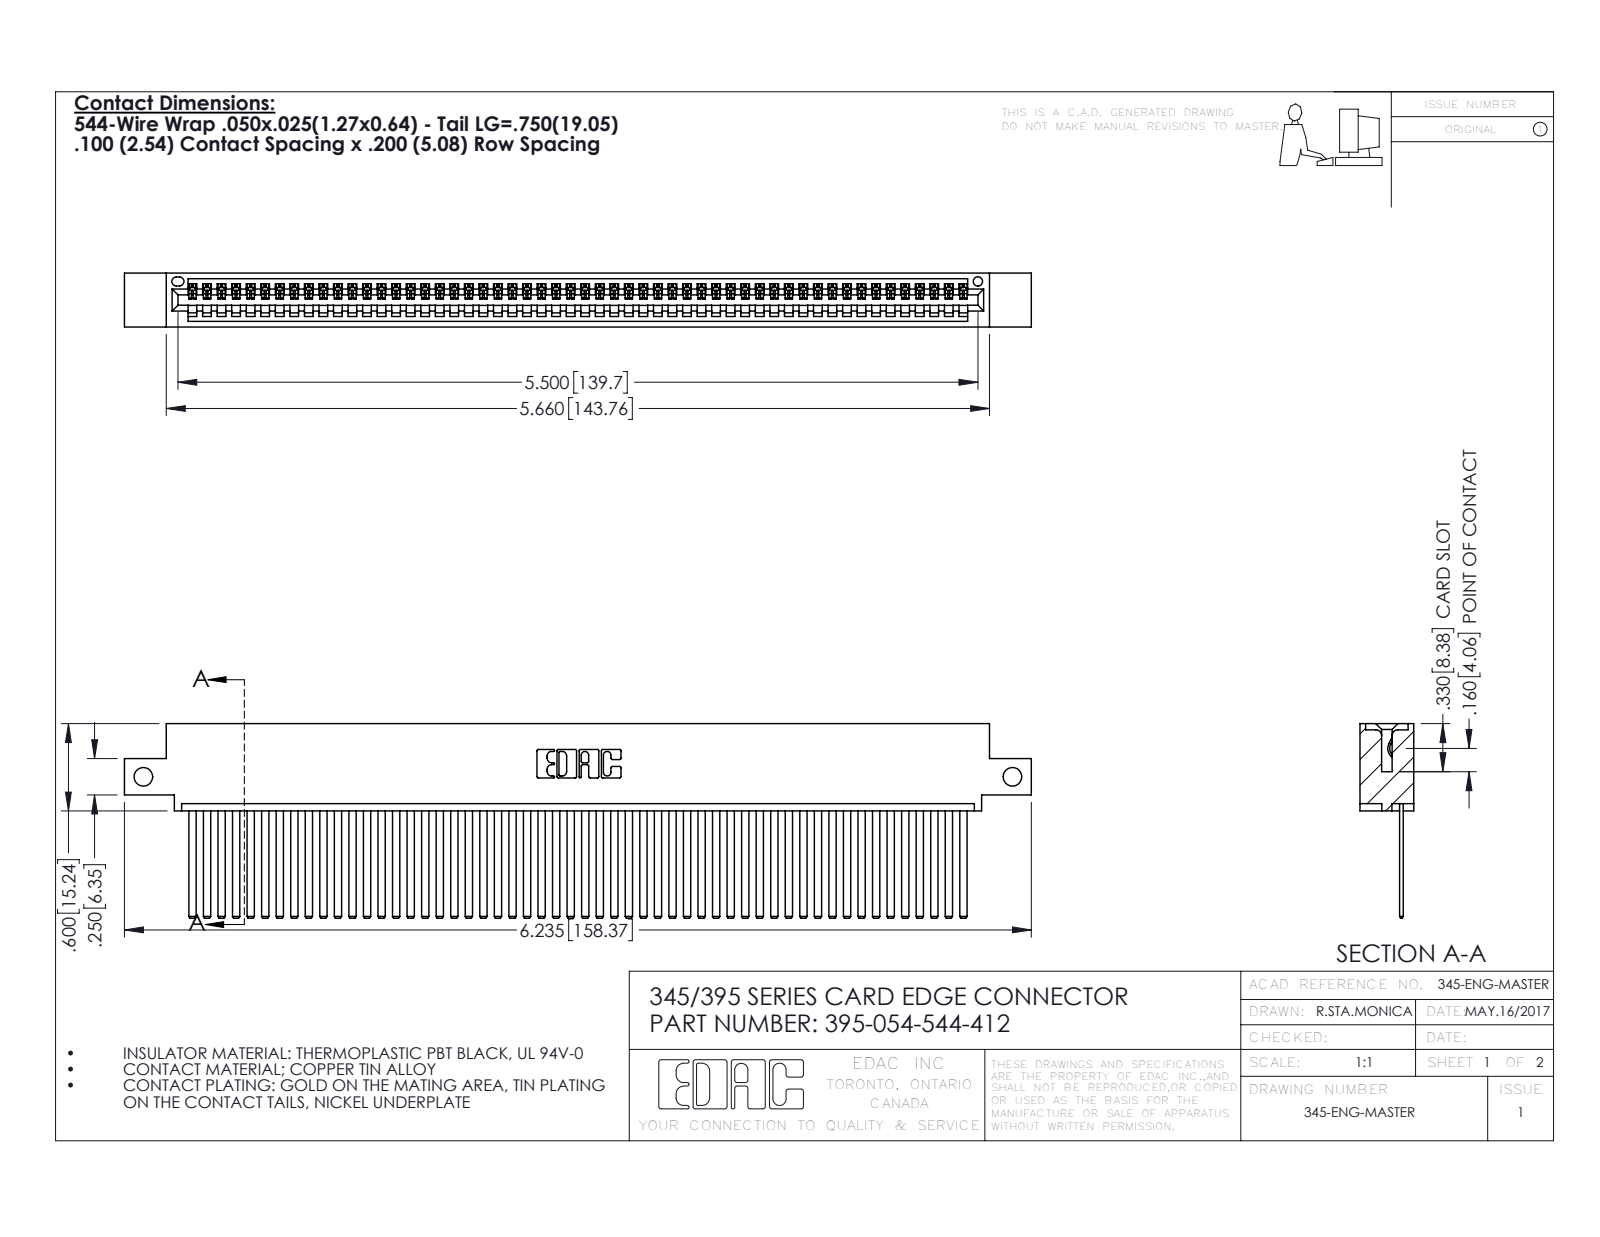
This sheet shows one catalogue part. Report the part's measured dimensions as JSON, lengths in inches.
{"part_name": "345-292-001_345-293-144; 395-054-544-412; 345 Part_0.110 Offset - Side Mount", "step_written_by": "SolidWorks 2016 (CONFIG_CONTROL_DESIGN)", "units": "inches", "bodies": {"solids": 55, "faces": 2938, "planar": 2028, "cylindrical": 910, "other": 0}, "overall_size": [6.235, 1.337, 0.37], "volume_in3": 0.952, "surface_area_in2": 35.21, "round_holes": [[0.128, 2], [0.064, 1]], "partial_cylinders_radius": [[0.006, 108], [0.01, 22], [0.007, 6], [0.031, 6], [0.026, 3], [0.031, 2], [0.04, 2], [0.014, 1]], "face_to_face_distances": [0.072, 0.298, 0.025, 0.098, 0.272, 0.37, 0.2, 0.225, 0.149, 0.072], "hole_center_spacings": [5.975]}
